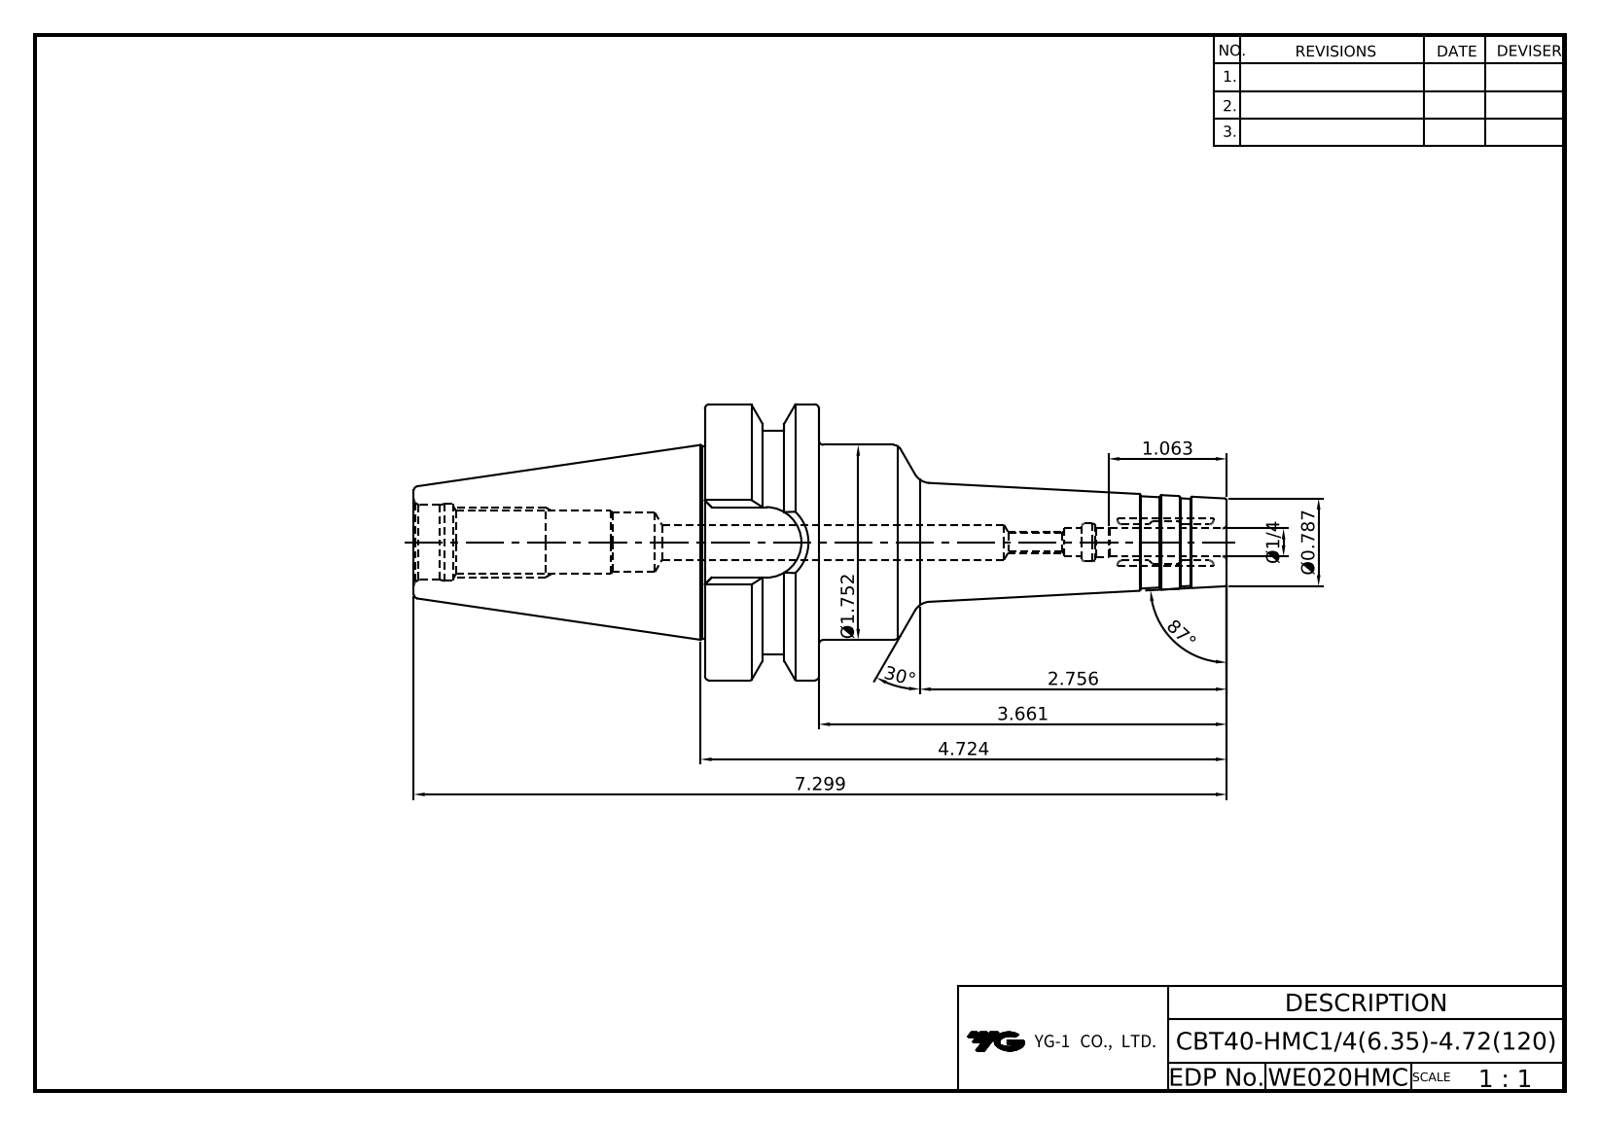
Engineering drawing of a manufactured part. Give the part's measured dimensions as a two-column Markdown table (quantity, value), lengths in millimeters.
| quantity | value |
| --- | --- |
| part name | LO-CBT40-HMC6.35-120 |
| STEP written by | Autodesk Inventor 2022 (AUTOMOTIVE_DESIGN) |
| units | millimeters |
| bodies | 1 solid, 87 faces (25 planar, 18 cylindrical, 44 other) |
| overall size | 185.4 × 63 × 63 |
| volume | 183 018 mm³ |
| surface area | 31 928 mm² |
| round holes (diameter × count) | 4.3 × 1, 6.35 × 1, 6.8 × 1, 8 × 1, 12 × 1, 13.5 × 1, 13.84 × 1, 17 × 1, 17.6 × 1 |
| round bosses / shafts (diameter × count) | 63 × 1, 52.6 × 1, 44.5 × 1, 44 × 1 |
| partial cylindrical surfaces (radius × count) | 8.05 × 1 |
| main face-to-face distances | 26, 119, 93, 0.4, 25.6, 118.6, 45.2, 16.1, 66.4, 66.8 |
